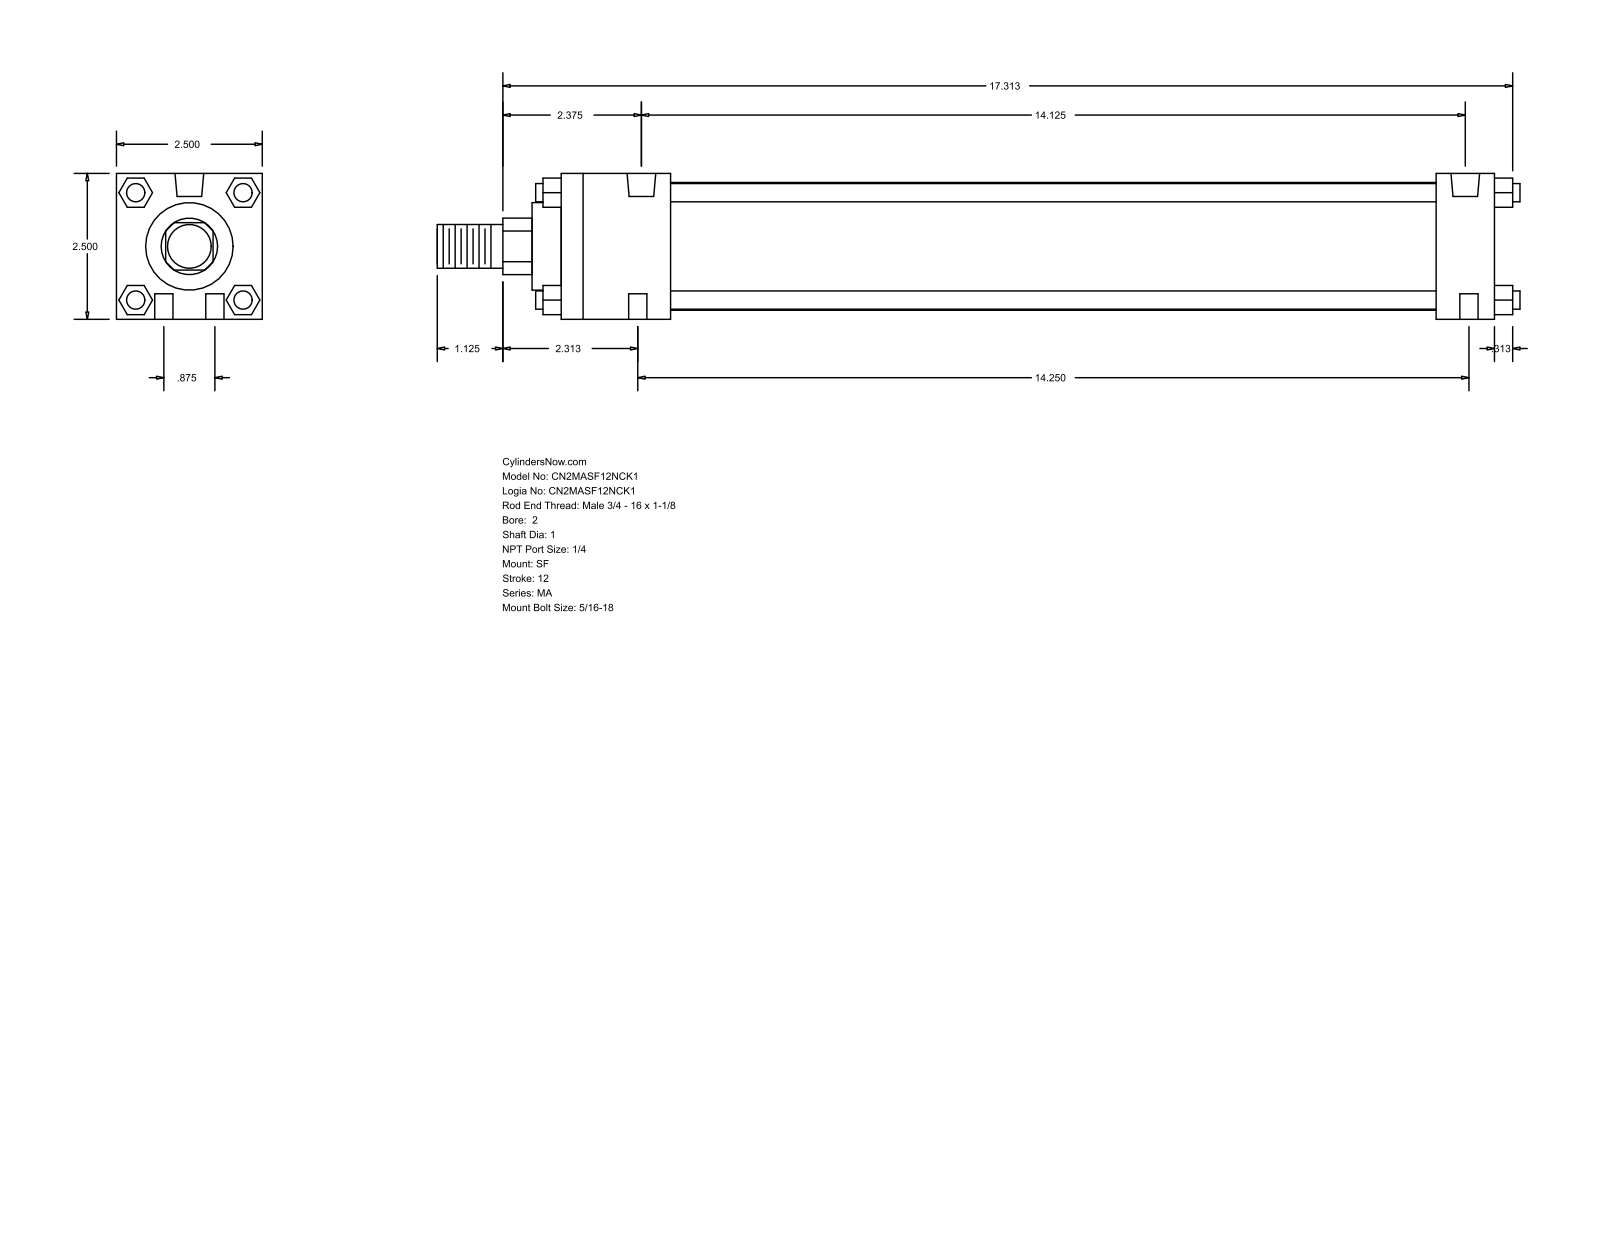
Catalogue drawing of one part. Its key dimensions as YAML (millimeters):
part_name: "MA_SF__0200_1"
step_written_by: "GSSL Pune (CONFIG_CONTROL_DESIGN)"
units: millimeters
bodies: {solids: 0, faces: 124, planar: 94, cylindrical: 30, other: 0}
overall_size: [471.49, 63.5, 63.5]
round_holes:
  - {diameter: 7.94, count: 6}
  - {diameter: 12.49, count: 2}
round_bosses_or_shafts:
  - {diameter: 7.94, count: 4}
  - {diameter: 55.63, count: 1}
  - {diameter: 38.1, count: 1}
  - {diameter: 25.4, count: 1}
  - {diameter: 19.05, count: 1}
partial_cylinders:
  - {radius: 12.29, count: 1}
face_to_face_distances: [63.5, 406.4, 12.7, 25.4, 381, 47.63, 333.37, 358.77, 23.37, 40.47]
hole_center_spacings: [11.22, 360.53, 22.22, 358.77, 361.95, 362.63]
